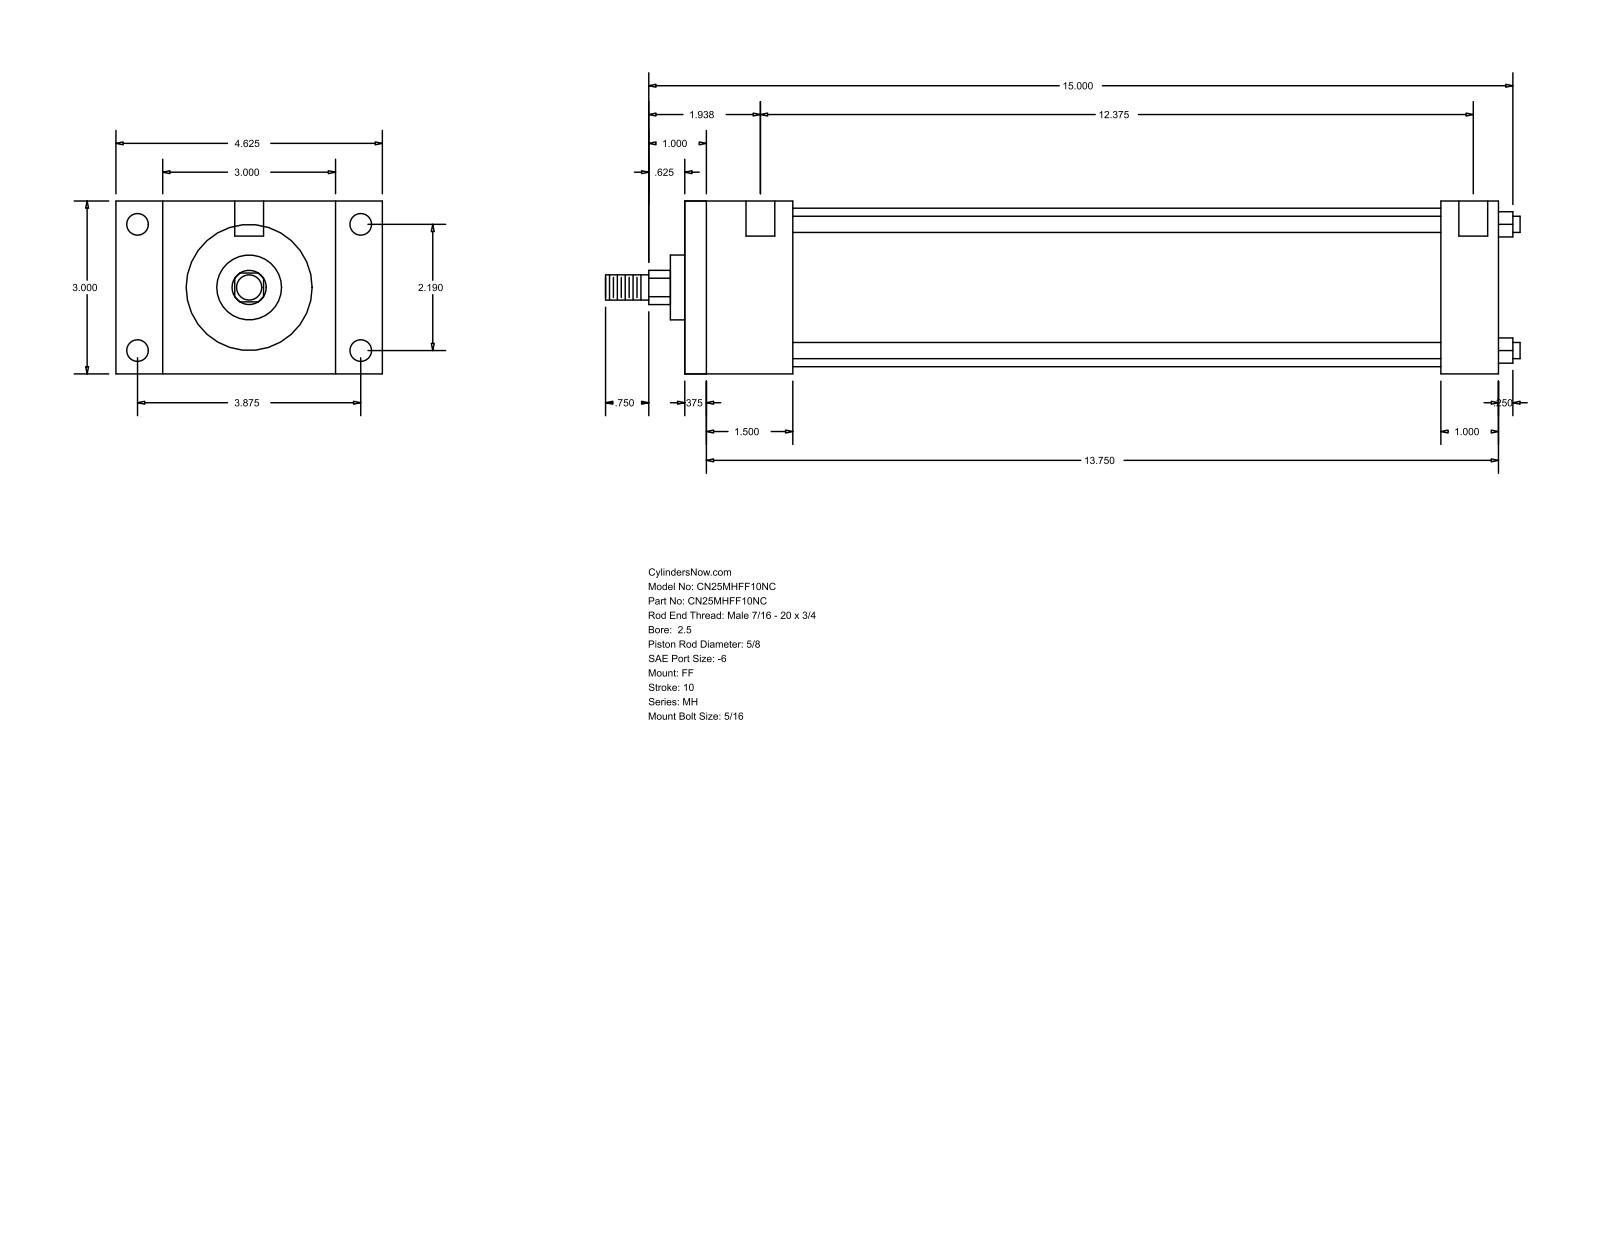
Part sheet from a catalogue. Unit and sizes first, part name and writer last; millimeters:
Units: millimetres
Overall size (bounding box): 403.23 × 117.47 × 76.2
Round holes (diameter × count): ⌀5.56 ×4, ⌀9.53 ×4, ⌀12.7 ×2
Round bosses / shafts (diameter × count): ⌀7.14 ×4, ⌀69.85 ×1, ⌀28.57 ×1, ⌀15.88 ×1, ⌀11.11 ×1
Partial cylindrical surfaces — rounded edges, fillets, slot ends (radius × count): R7.54 ×1
Main face-to-face distances: 76.2, 358.77, 349.25, 9.52, 25.4, 47.62, 333.37, 38.1, 323.85, 285.75
Hole centre spacings: 55.62, 98.42, 113.05, 322.26, 3.17, 4.76, 314.33, 317.5
Bodies: 0 solids, 92 faces (64 planar, 28 cylindrical, 0 other)
Part name (STEP PRODUCT): MH_FF__0250_0.625
STEP written by: GSSL Pune (CONFIG_CONTROL_DESIGN)
